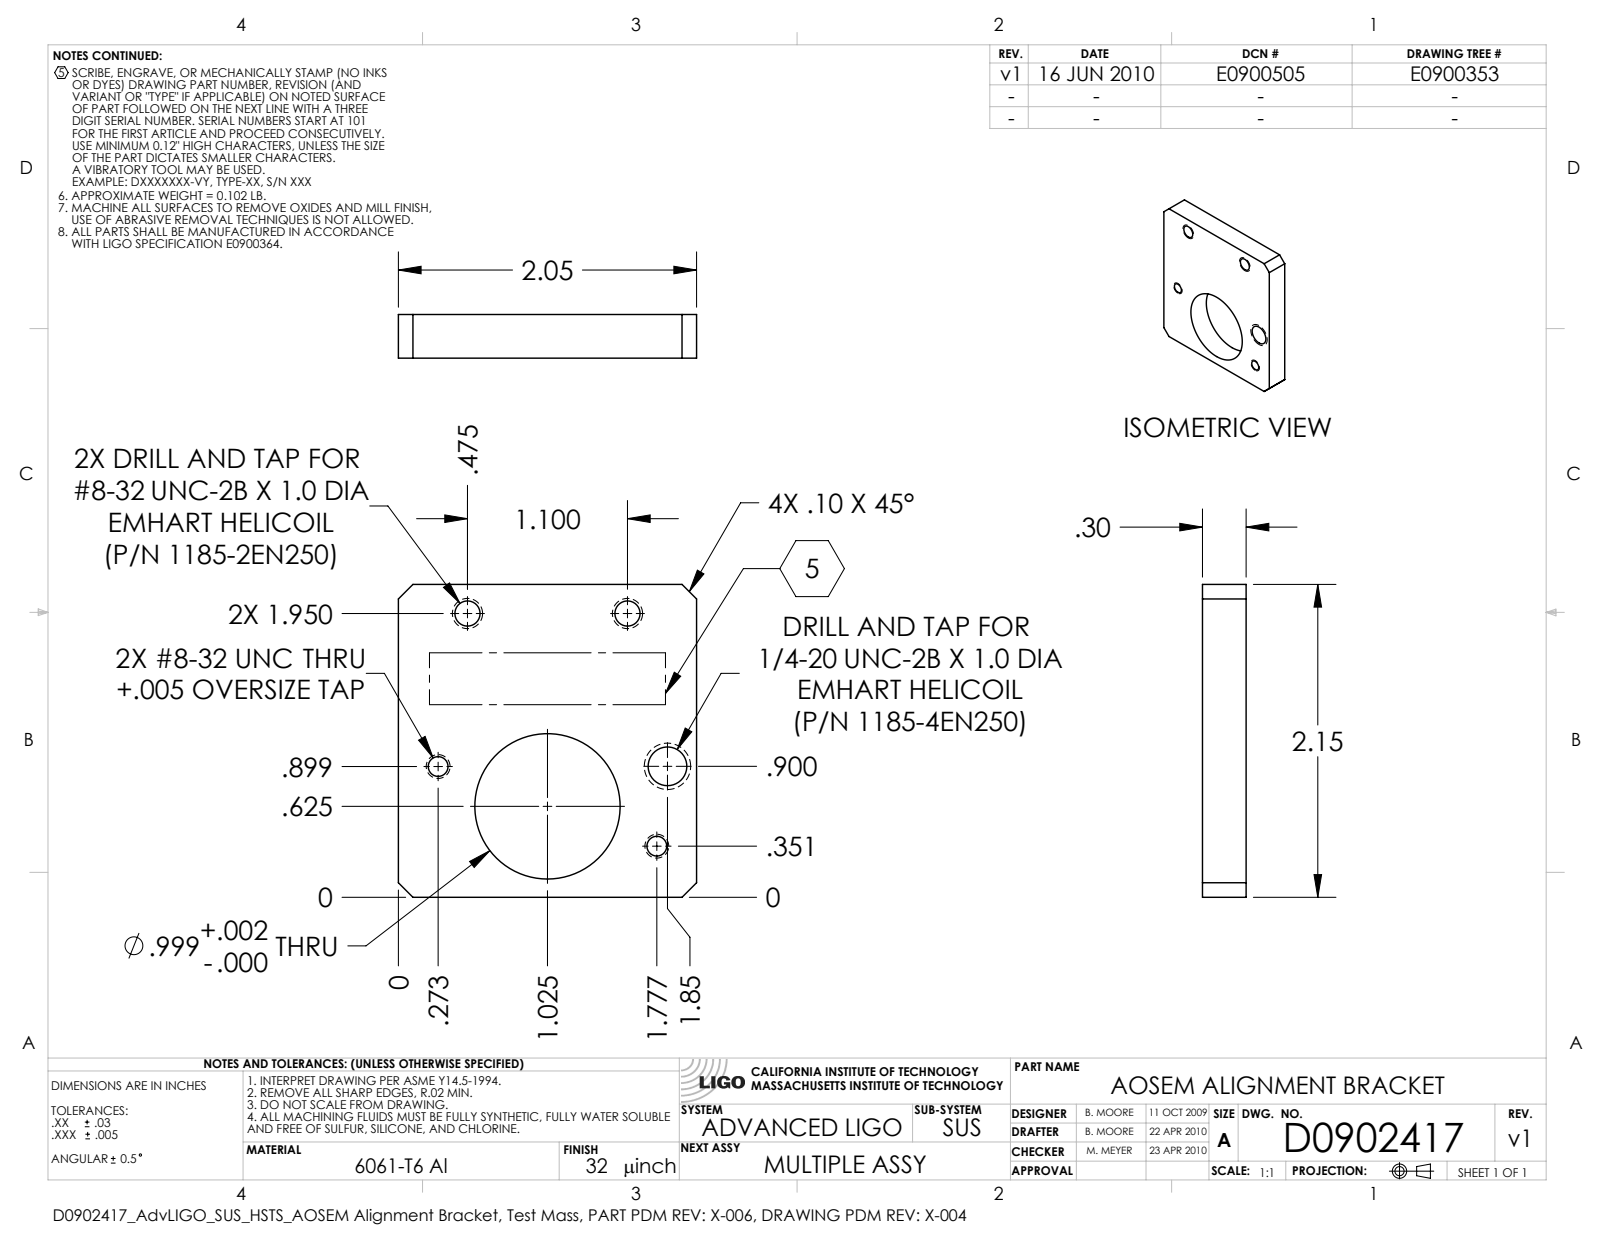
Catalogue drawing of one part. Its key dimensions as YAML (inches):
part_name: "D0902417-v1_aLIGO_SUS_HSTS_AOSEM Alignment Bracket, Test Mass"
step_written_by: "SolidWorks 2010 (CONFIG_CONTROL_DESIGN)"
units: inches
bodies: {solids: 1, faces: 22, planar: 10, cylindrical: 12, other: 0}
overall_size: [2.15, 2.05, 0.3]
volume: 1.042
surface_area: 11.17
round_holes:
  - {diameter: 0.136, count: 2}
  - {diameter: 0.173, count: 2}
  - {diameter: 0.266, count: 1}
  - {diameter: 0.999, count: 1}
face_to_face_distances: [0.3, 2.05, 2.15, 2.828]
hole_center_spacings: [0.8, 1.434, 0.553, 0.87, 1.07, 1.085, 1.1, 1.577]
